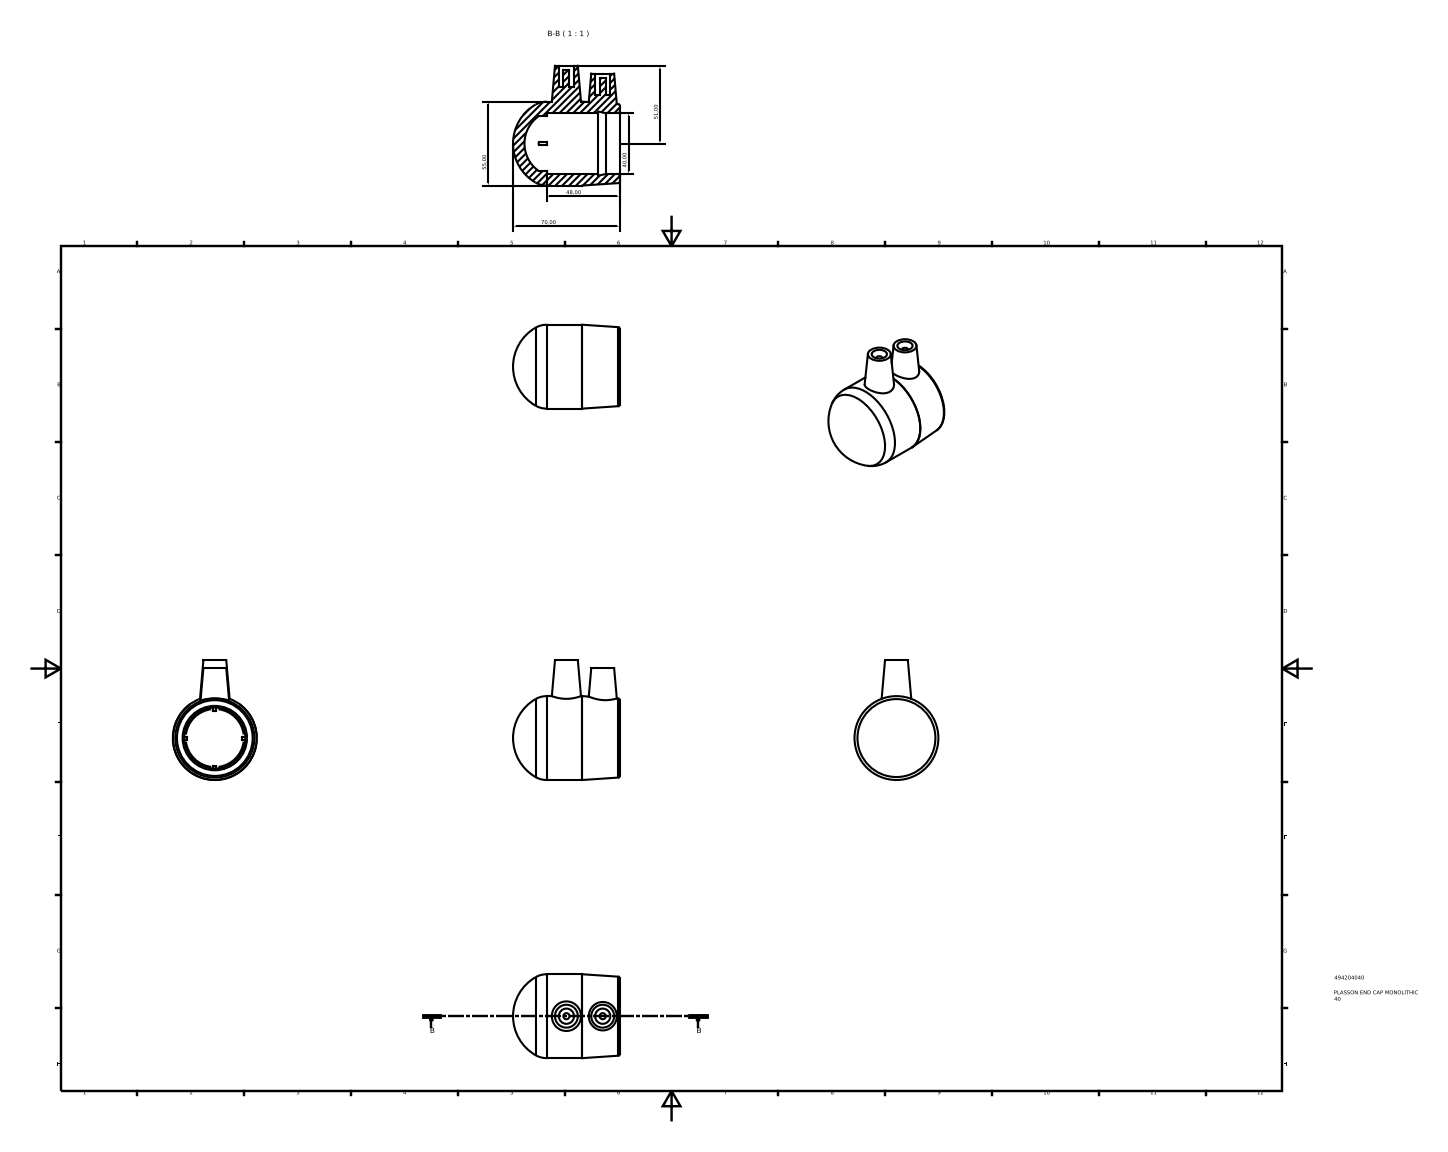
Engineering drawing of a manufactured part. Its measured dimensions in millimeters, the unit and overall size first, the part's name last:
Units: millimetres
Overall size (bounding box): 78.5 × 70 × 55
Round holes (diameter × count): ⌀10 ×2, ⌀40 ×1
Round bosses / shafts (diameter × count): ⌀4 ×2, ⌀55 ×1
Main face-to-face distances: 14, 5.1, 19.1, 8.9, 19, 17, 36, 2, 11, 3
Hole centre spacings: 23.8
Volume: 79 959 mm³ · Surface area: 24 459 mm²
Bodies: 1 solid, 45 faces (24 planar, 7 cylindrical, 14 other)
Part name (STEP PRODUCT): 494204040
STEP written by: Autodesk Inventor 2015 (AUTOMOTIVE_DESIGN)
